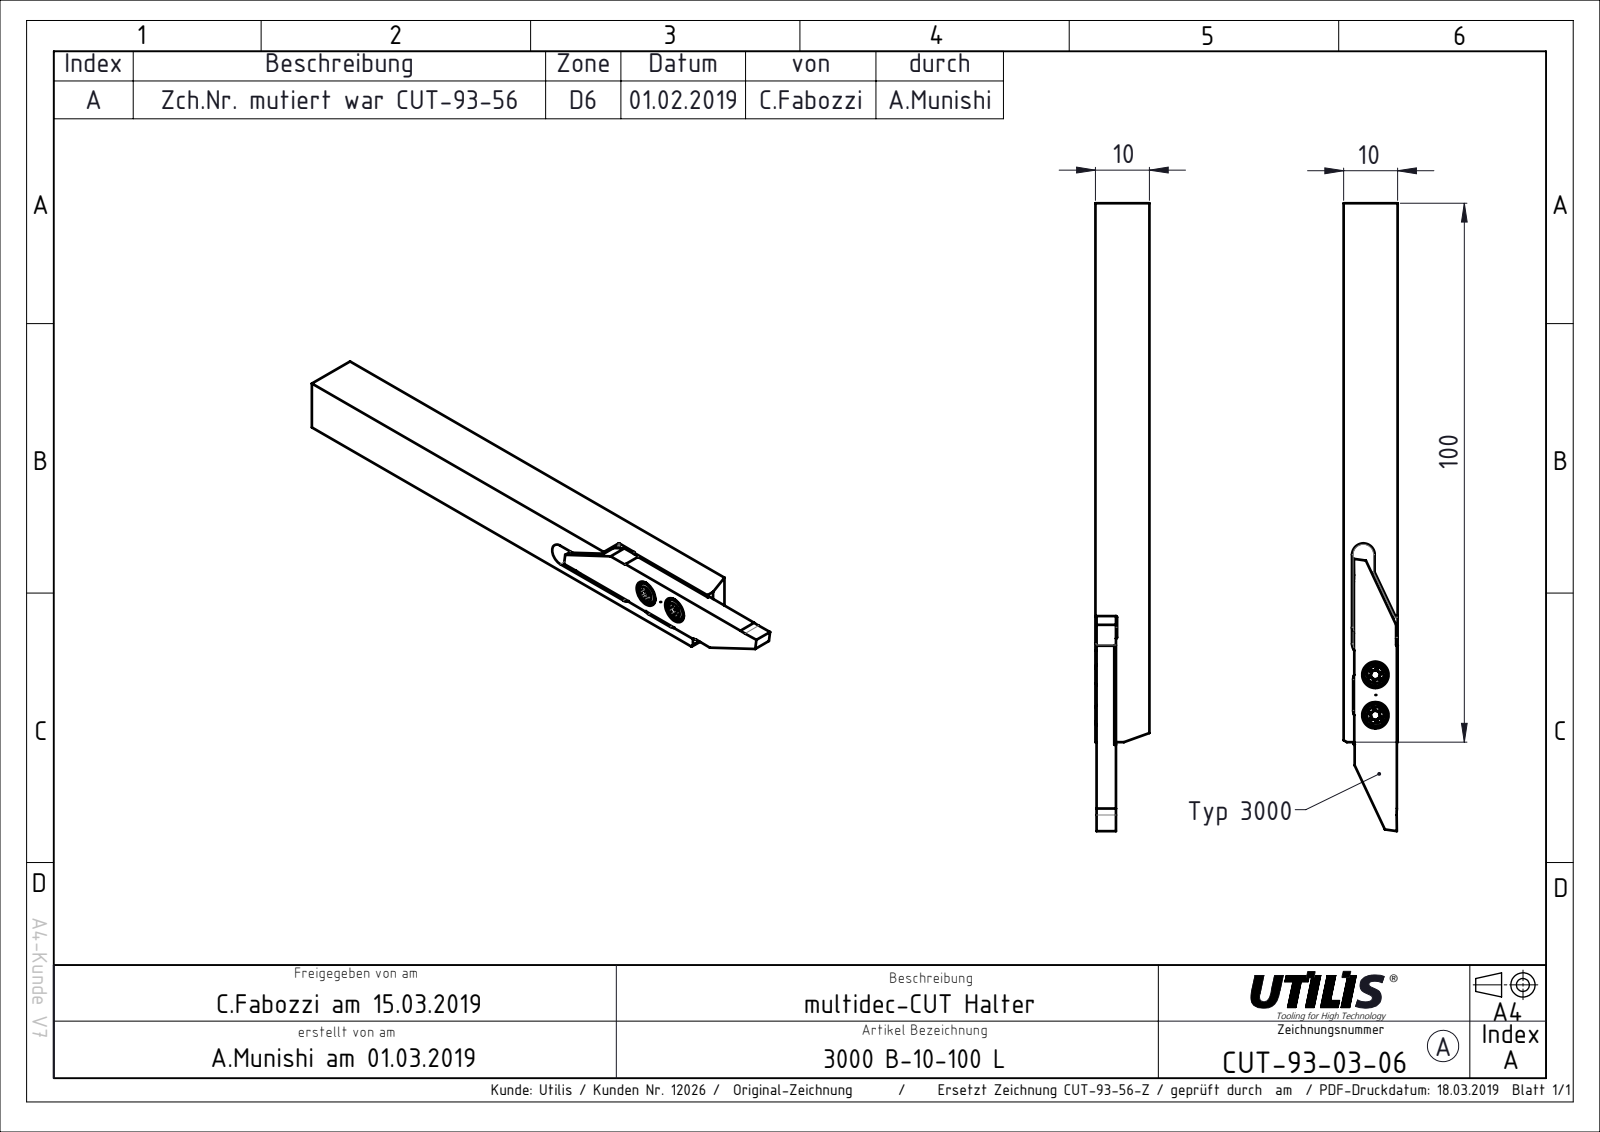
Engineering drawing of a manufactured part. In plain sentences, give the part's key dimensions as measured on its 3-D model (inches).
The part is named "CUT-93-56; CUT-Vorlage 3000 R+L Lang Kunde_L-Lang; CUT-Vorlage 3000 R+L Lang Kunde; CUT-93-Kunde_56 (+1 more)". Its 3-D file was written by "SolidWorks 2015 (CONFIG_CONTROL_DESIGN)". It is 2 solids with 55 faces: 36 planar, 19 cylindrical and 0 other. Overall it measures 4.587 by 0.394 by 0.394 inches. Its volume is 0.607 cubic inches and its surface area 8.389 square inches. Round holes: 2 of diameter 0.098, 2 of diameter 0.193. Partial cylindrical surfaces (rounded edges, fillets, slot ends): 4 of radius 0.083, 2 of radius 0.006, 2 of radius 0.394. The main face-to-face distances are 0.394, 0.15, 0.244, 0.142, 0.386, 0.079, 0.315, 0.061, 0.018, 0.333. The hole center spacings are 0.148, 0.295.
